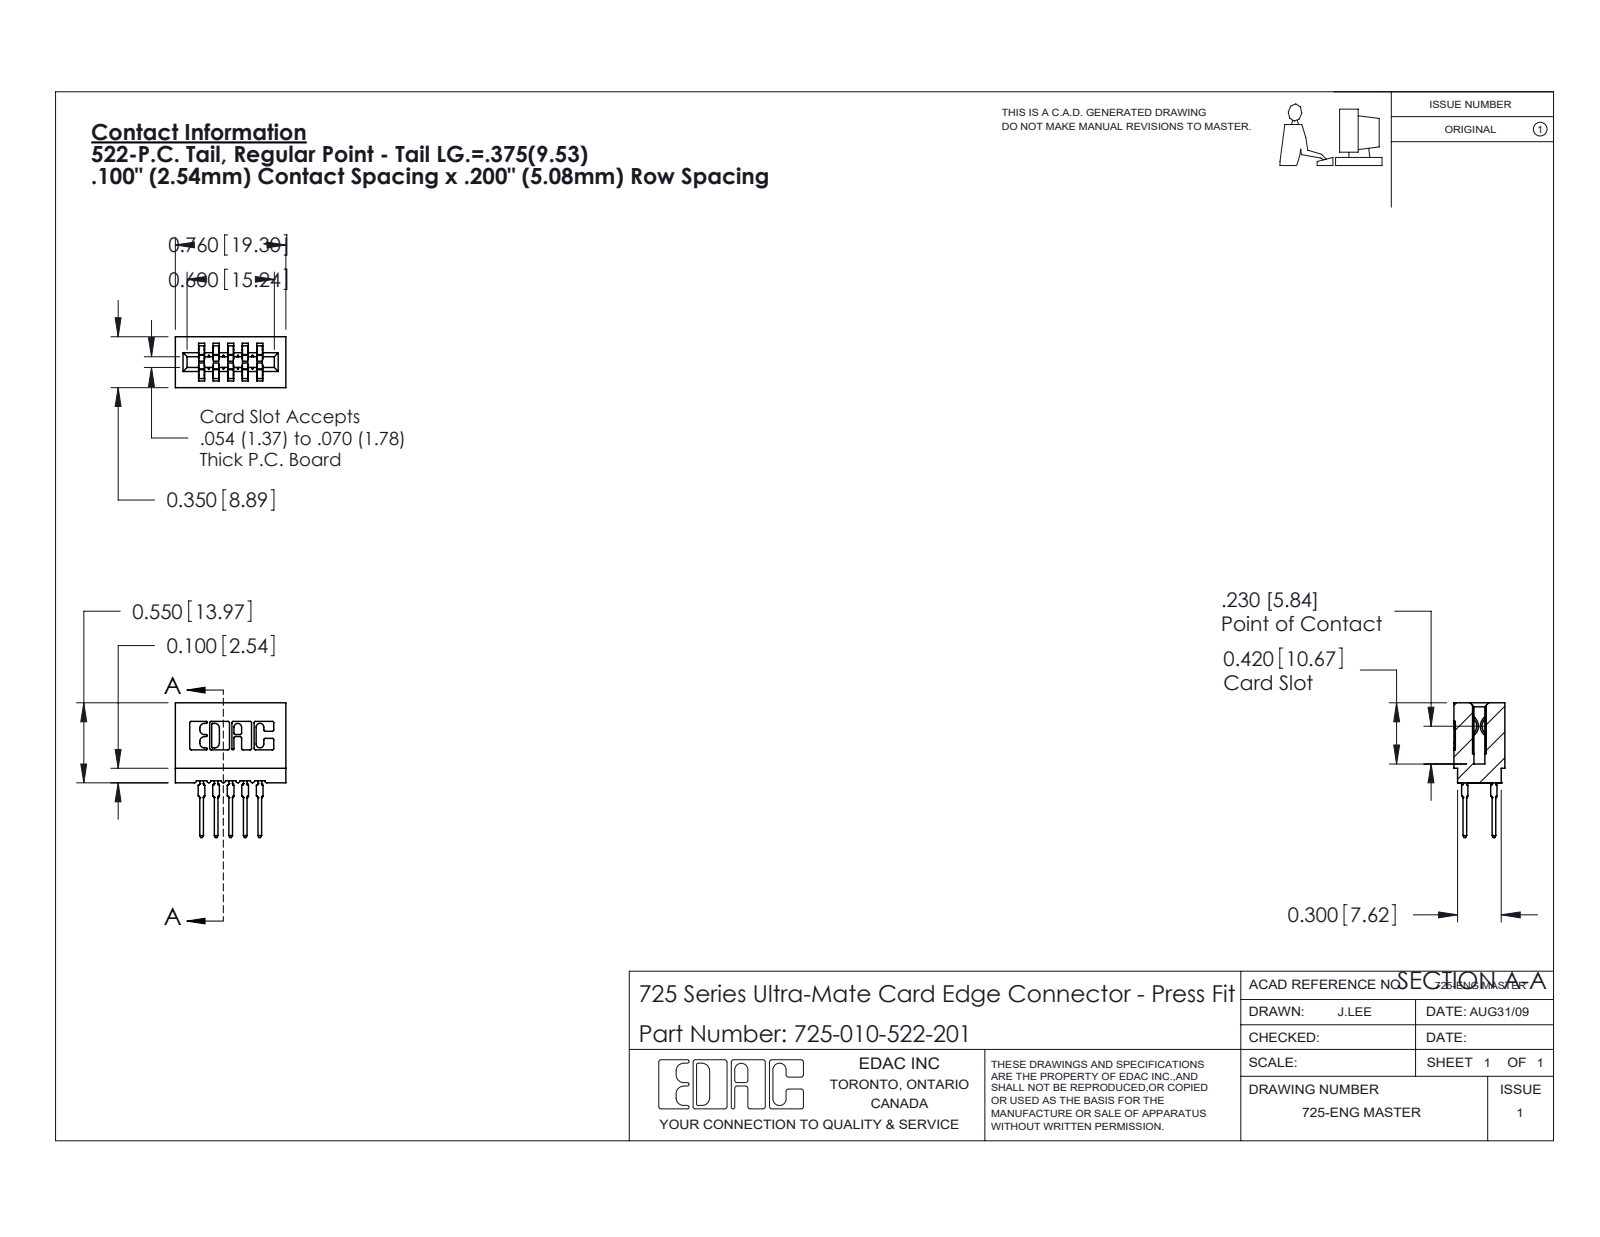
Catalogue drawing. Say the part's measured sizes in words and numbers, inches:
The part is named "725-010-522-201; 725 Part_Insulator Option - 01; 745-292-001_522". Its 3-D file was written by "SolidWorks 2020 (CONFIG_CONTROL_DESIGN)". It is 11 solids with 990 faces: 515 planar, 215 cylindrical and 260 other. Overall it measures 0.926 by 0.76 by 0.35 inches. Its volume is 0.105 cubic inches and its surface area 4.487 square inches. Partial cylindrical surfaces (rounded edges, fillets, slot ends): 22 of radius 0.01, 20 of radius 0.021, 10 of radius 0.015, 8 of radius 0.005, 8 of radius 0.011, 6 of radius 0.007, 6 of radius 0.031, 3 of radius 0.026. The main face-to-face distances are 0.1, 0.2, 0.042, 0.3, 0.142, 0.058, 0.287, 0.242, 0.158, 0.212.
